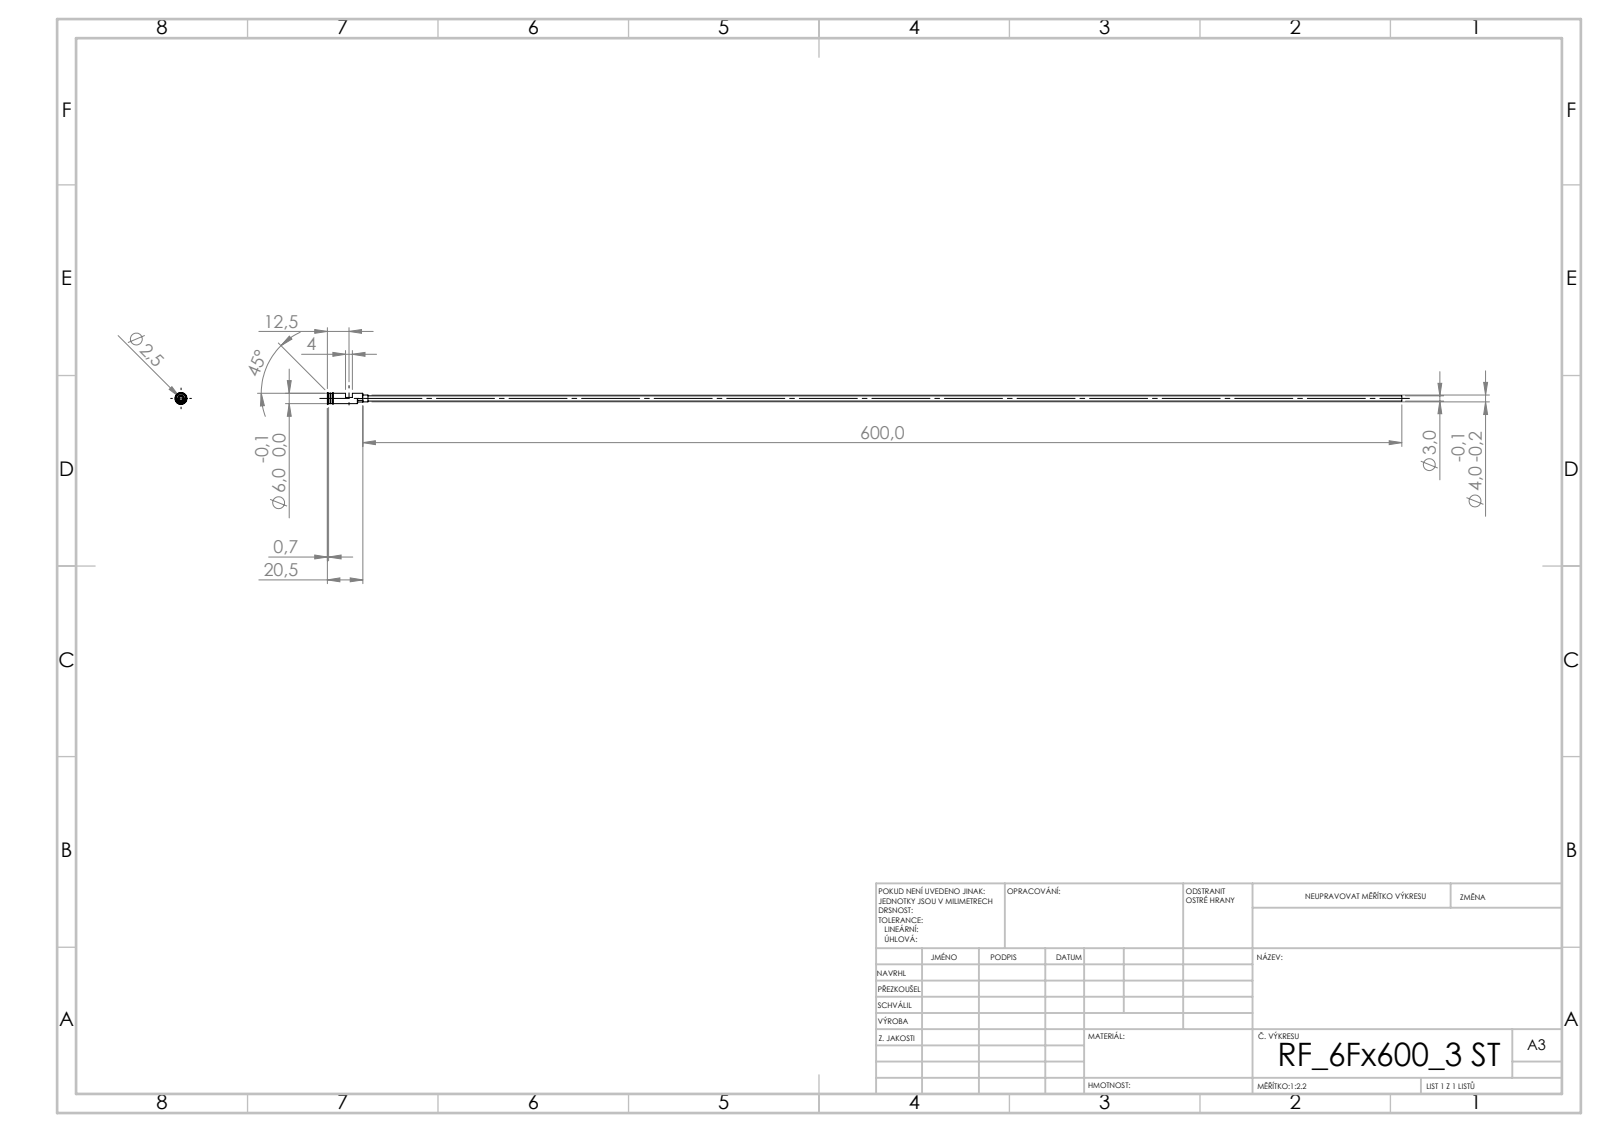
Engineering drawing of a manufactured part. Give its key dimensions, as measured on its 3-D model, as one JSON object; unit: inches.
{"step_written_by": "SolidWorks 2019 (CONFIG_CONTROL_DESIGN)", "units": "inches", "bodies": {"solids": 1, "faces": 55, "planar": 24, "cylindrical": 19, "other": 12}, "overall_size": [24.429, 0.276, 0.276], "volume_in3": 0.109, "surface_area_in2": 16.93, "round_holes": [[0.098, 1]], "round_bosses_or_shafts": [[0.276, 1], [0.236, 1], [0.228, 1], [0.157, 1], [0.118, 1]], "partial_cylinders_radius": [[0.118, 2], [0.081, 1]], "face_to_face_distances": [0.118, 0.413, 0.236, 0.571, 0.079, 0.157, 0.807, 0.394, 0.276, 0.689]}
